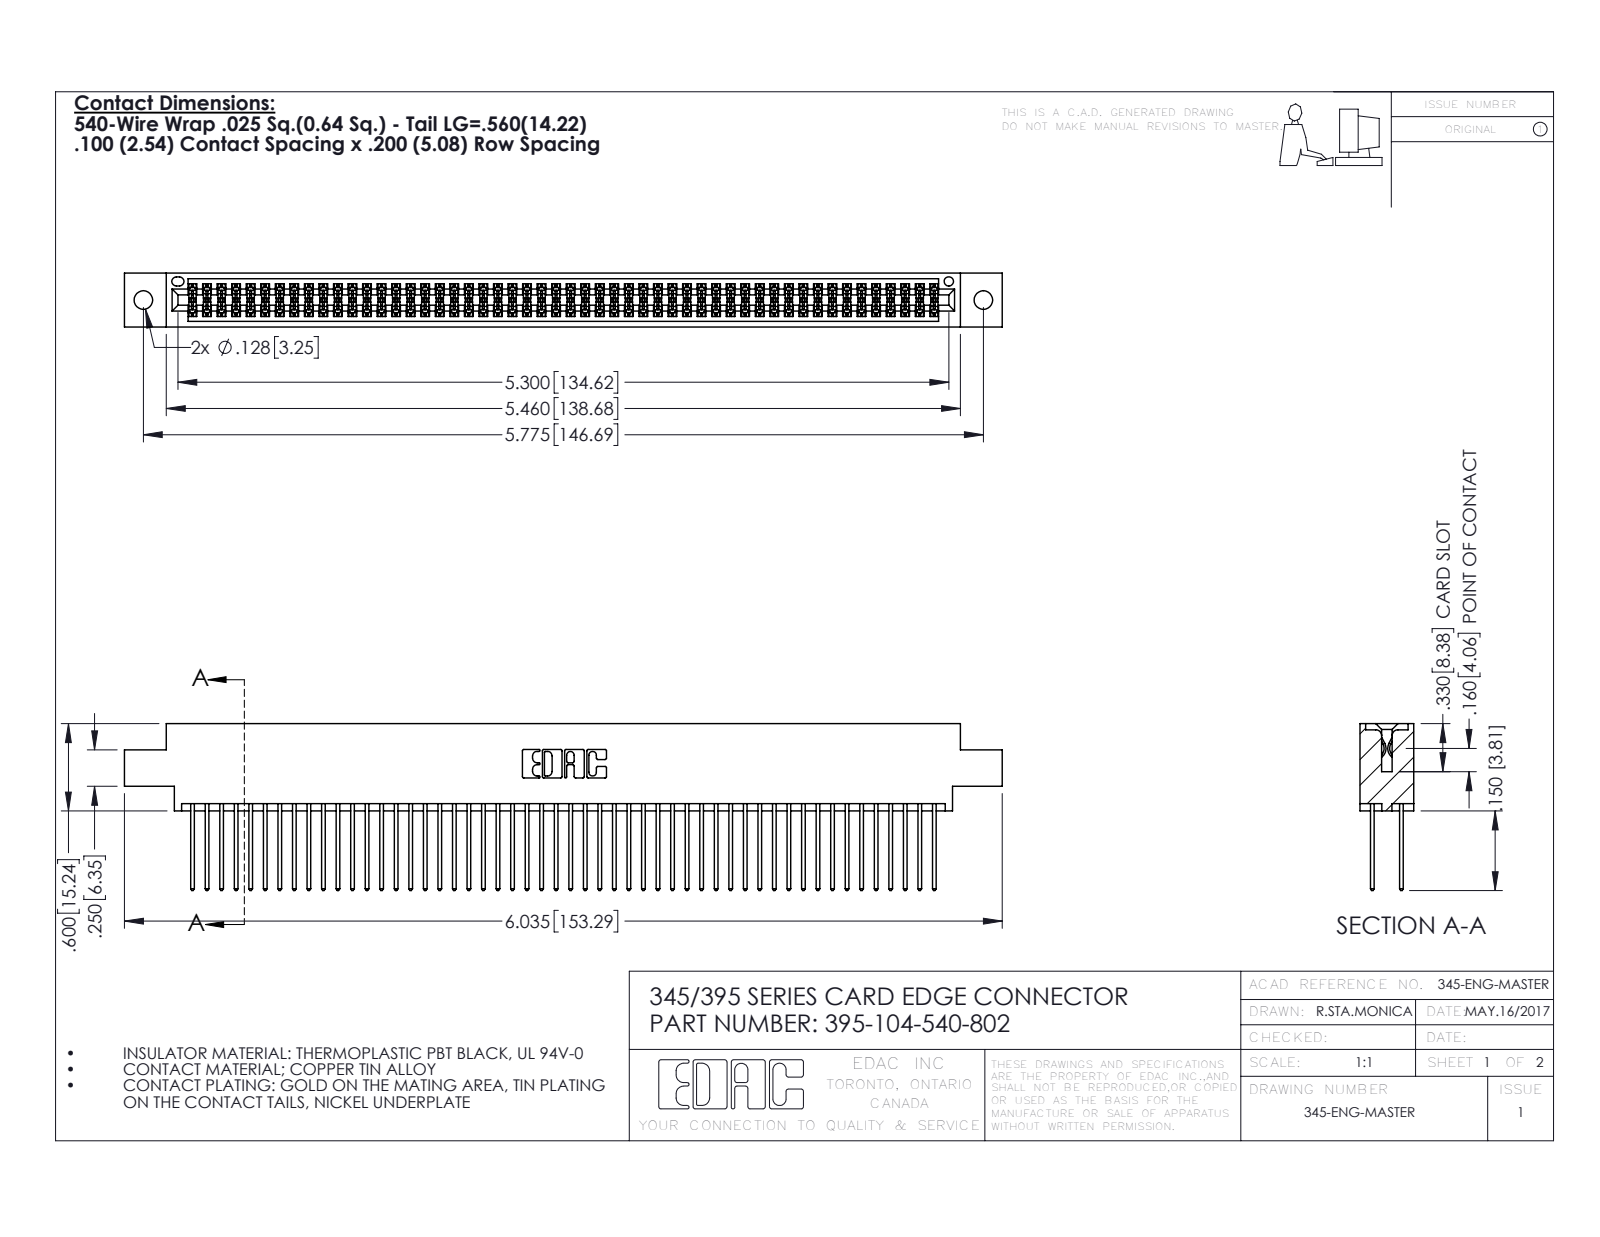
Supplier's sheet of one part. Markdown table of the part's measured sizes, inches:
| quantity | value |
| --- | --- |
| part name | 345-292-001_345-293-140; 395-104-540-802; 345 Part_0.170 Offset - 0.128 Dia |
| STEP written by | SolidWorks 2016 (CONFIG_CONTROL_DESIGN) |
| units | inches |
| bodies | 105 solids, 5330 faces (3516 planar, 1814 cylindrical, 0 other) |
| overall size | 6.035 × 1.147 × 0.37 |
| volume | 0.929 in³ |
| surface area | 37.82 in² |
| round holes (diameter × count) | 0.128 × 2, 0.064 × 1 |
| partial cylindrical surfaces (radius × count) | 0.006 × 156, 0.01 × 104, 0.01 × 22, 0.007 × 6, 0.031 × 6, 0.026 × 3, 0.014 × 2, 0.019 × 2 |
| main face-to-face distances | 0.298, 0.072, 0.2, 0.098, 0.272, 0.025, 0.37, 0.225, 0.175, 0.149 |
| hole center spacings | 0.27, 5.539, 5.775 |
